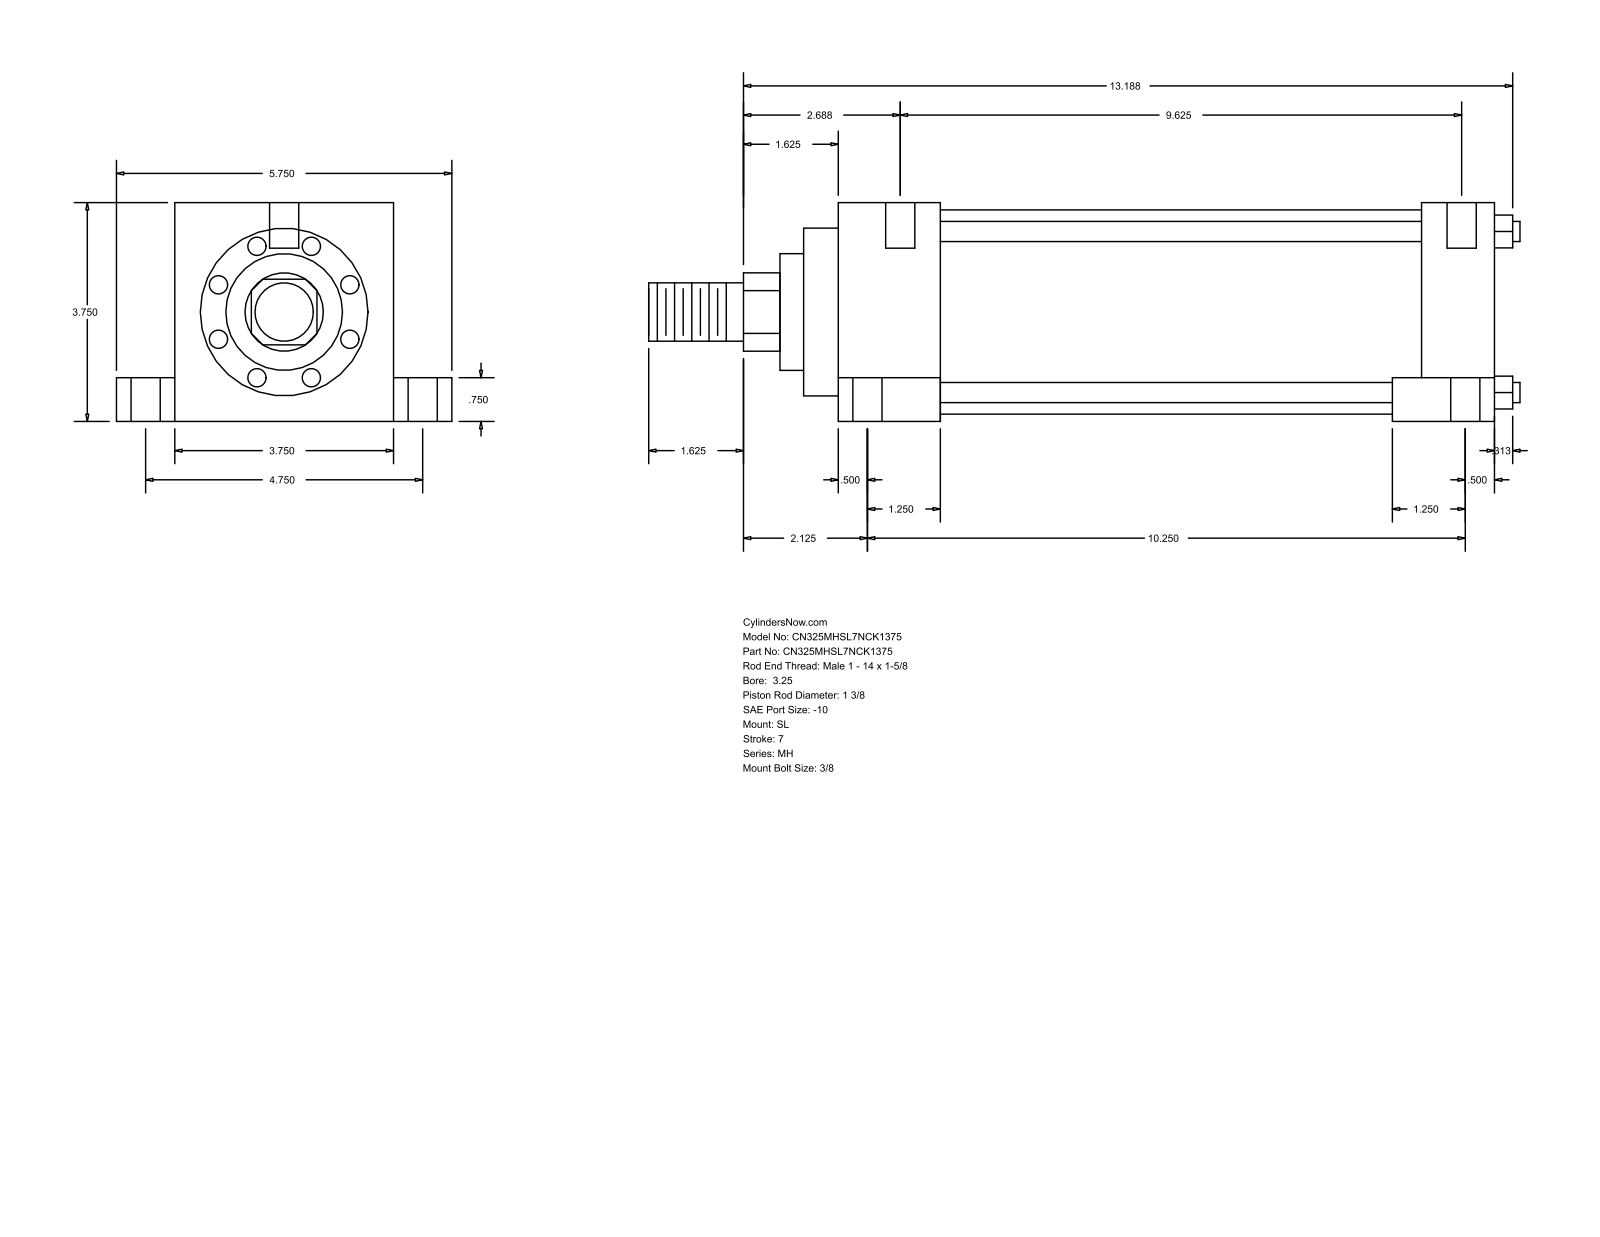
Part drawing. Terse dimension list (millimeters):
name: MH_SL__0325_1.375
written by: GSSL Pune (CONFIG_CONTROL_DESIGN)
unit: mm
bodies: 0 solids, 110 faces (77 planar, 33 cylindrical, 0 other)
size: 379.41 × 146.05 × 95.25
holes: 6× ⌀12.7, 4× ⌀5.56, 4× ⌀19.05
bosses: 4× ⌀8.76, 1× ⌀88.9, 1× ⌀73.03, 1× ⌀50.8, 1× ⌀34.92, 1× ⌀25.4
rounds: 1× R17.06
face distances: 95.24, 285.75, 44.45, 241.3, 25.41, 120.65, 19.05, 76.19, 254, 209.55
hole spacings: 60.35, 60.41, 61.65, 62, 120.66, 250.83, 253.35, 254.89
